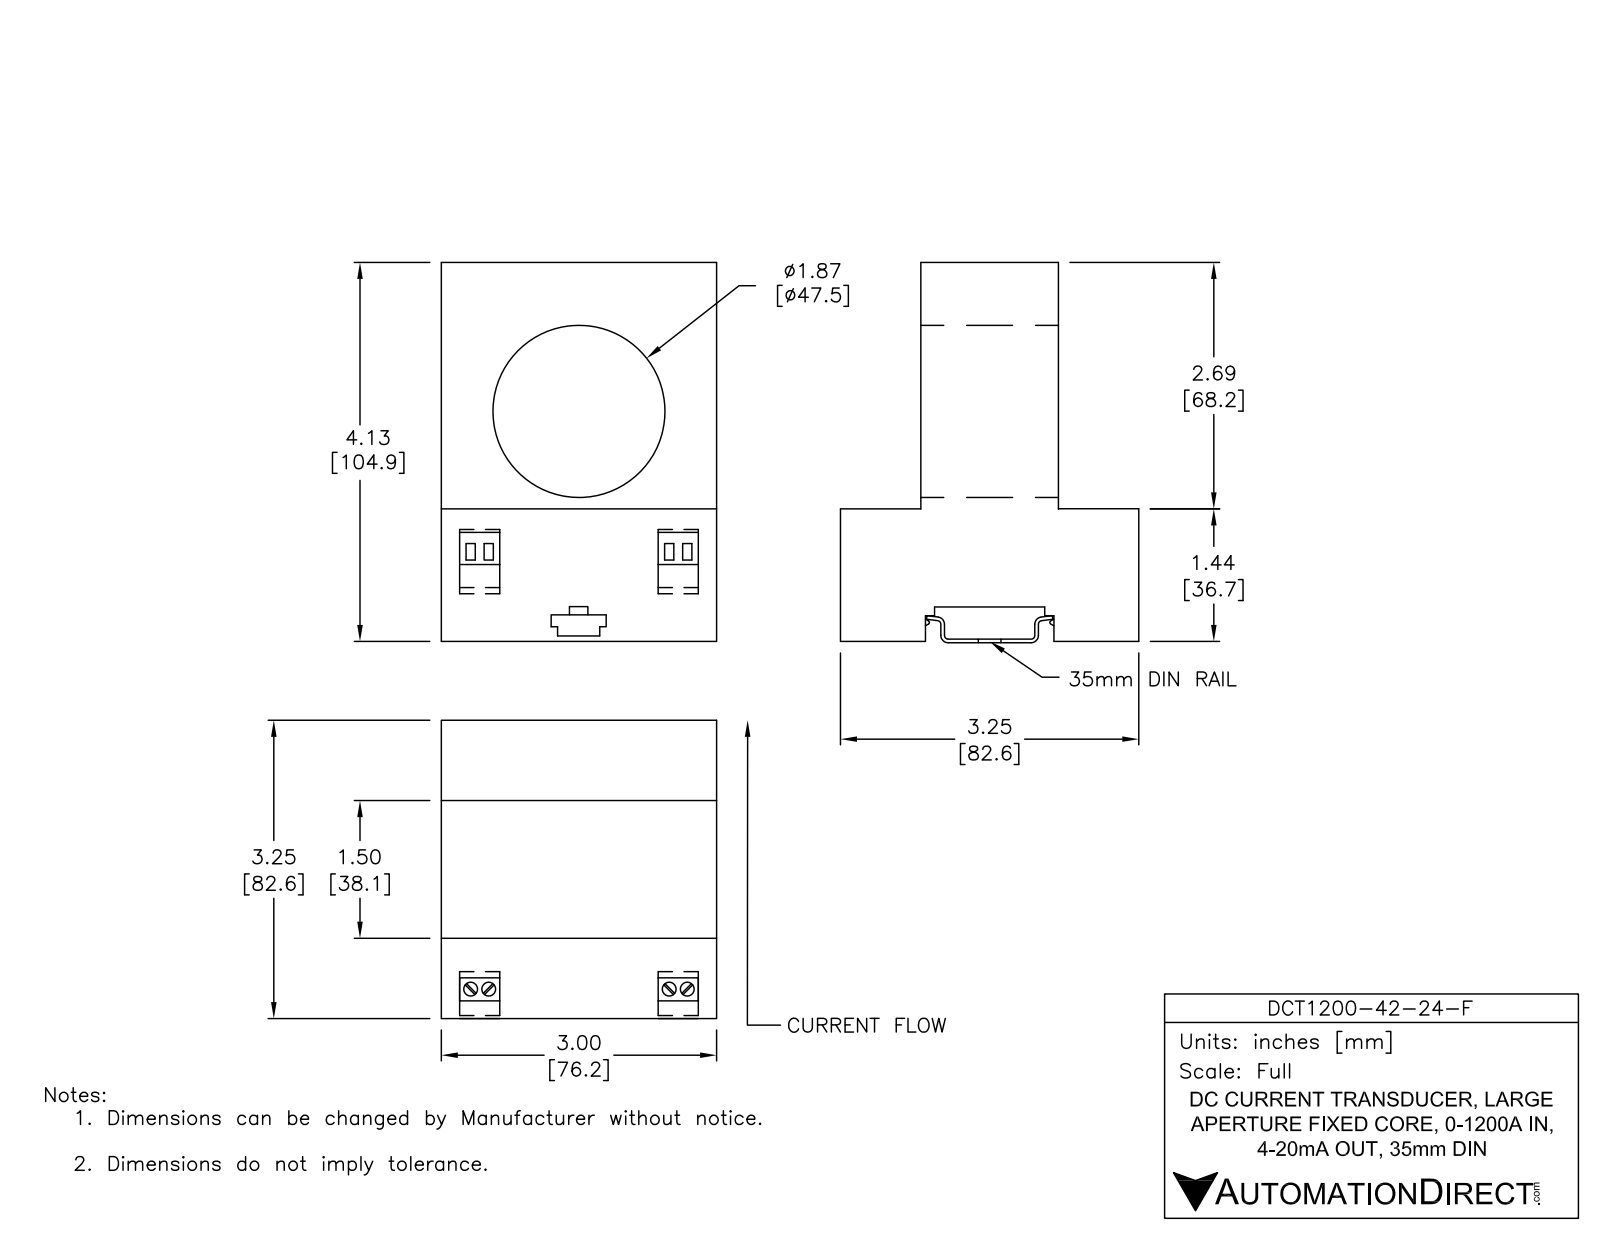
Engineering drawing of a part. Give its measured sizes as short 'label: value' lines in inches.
name: DCT1200-42-24-F
written by: SolidWorks 2017 (AUTOMOTIVE_DESIGN)
unit: in
bodies: 13 solids, 360 faces (310 planar, 50 cylindrical, 0 other)
size: 4.2 × 3.524 × 3
volume: 14.05 in³; area: 110.2 in²
holes: 4× ⌀0.206, 2× ⌀0.1, 1× ⌀1.82
bosses: 4× ⌀0.186
rounds: 4× R0.099, 4× R0.128, 4× R0.177
face distances: 0.075, 0.075, 3, 1.206, 1.131, 1.5, 1.25, 1.175, 0.044, 2.37
hole spacings: 0.394, 1.736, 2.574, 2.704, 0.676, 0.676, 1.068, 1.068
